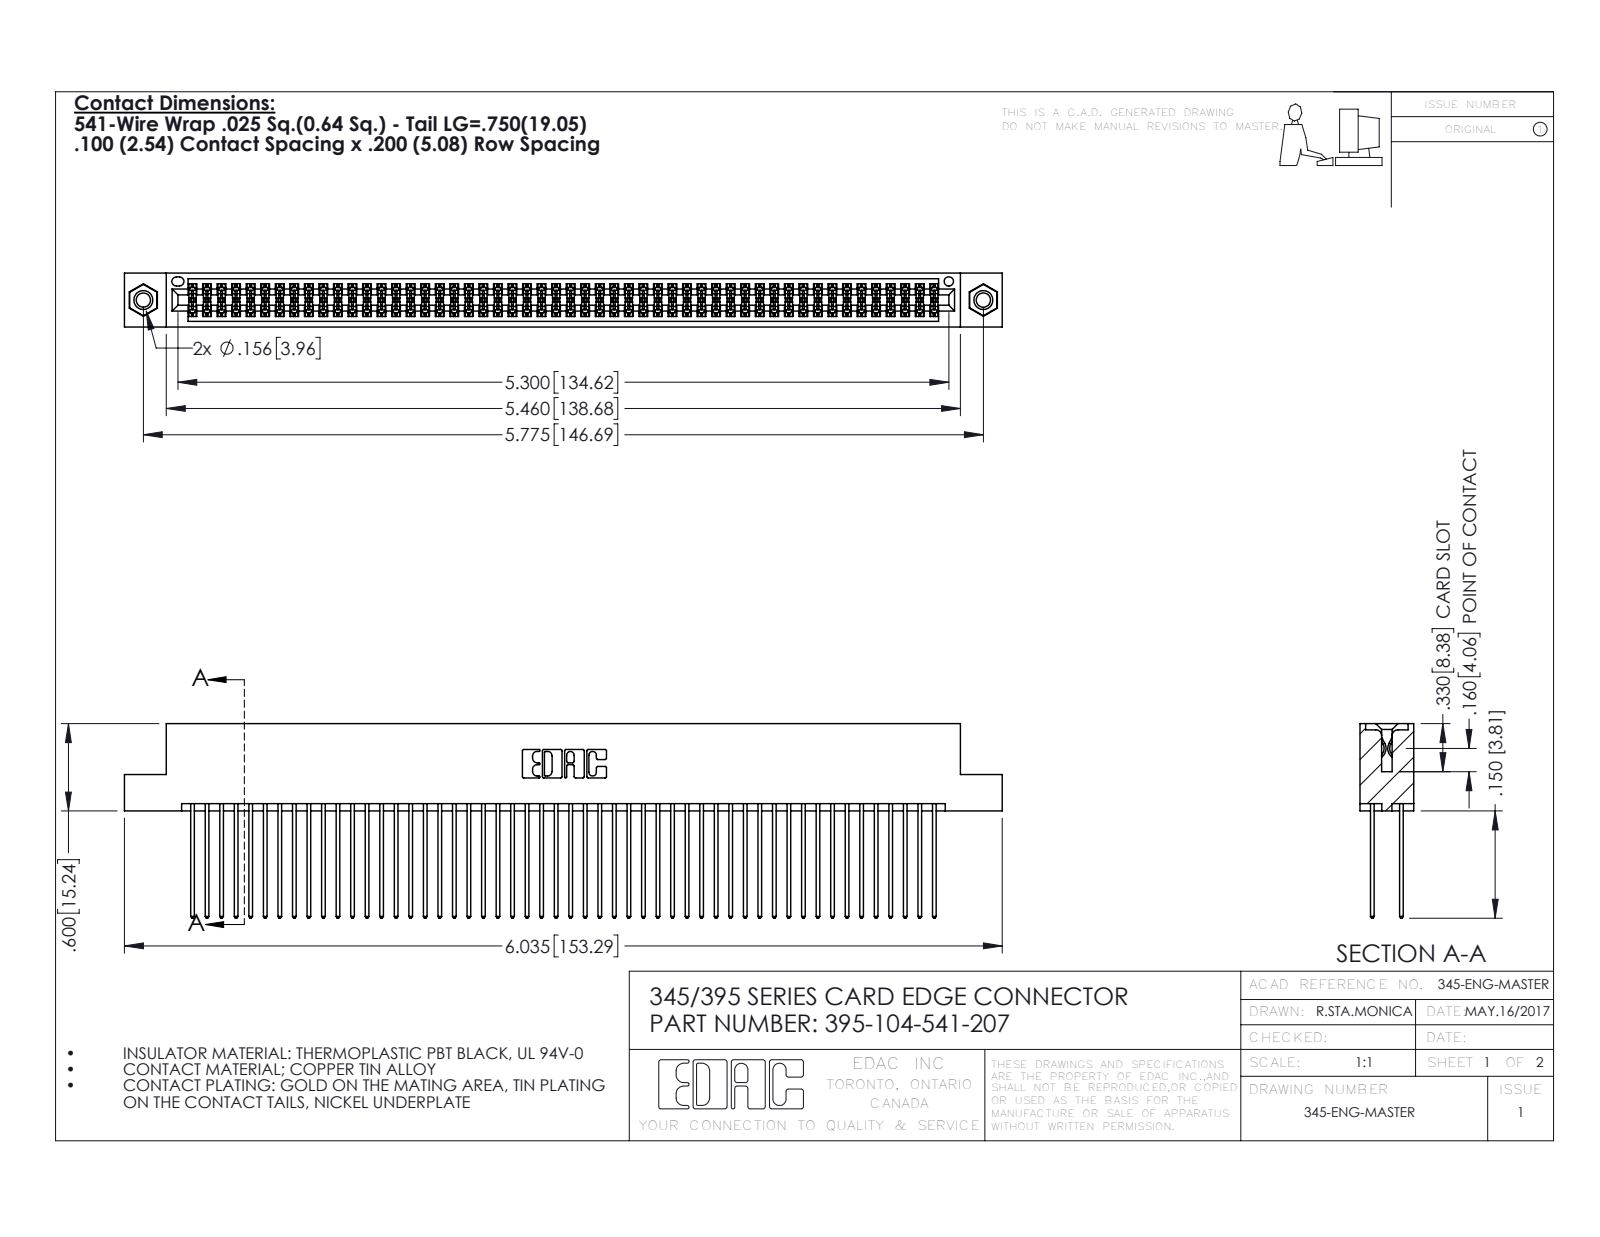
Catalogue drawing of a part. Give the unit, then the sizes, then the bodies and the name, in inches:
Units: inches
Overall size (bounding box): 6.035 × 1.337 × 0.37
Round holes (diameter × count): ⌀0.098 ×2, ⌀0.125 ×2, ⌀0.156 ×2, ⌀0.064 ×1
Round bosses / shafts (diameter × count): ⌀0.155 ×2
Partial cylindrical surfaces — rounded edges, fillets, slot ends (radius × count): R0.006 ×156, R0.01 ×104, R0.01 ×22, R0.007 ×6, R0.031 ×6, R0.026 ×3, R0.014 ×2, R0.019 ×2
Main face-to-face distances: 0.072, 0.298, 0.2, 0.098, 0.272, 0.025, 0.225, 0.37, 0.175, 0.149
Hole centre spacings: 0.27, 5.539, 5.775
Volume: 0.95 in³ · Surface area: 40.36 in²
Bodies: 107 solids, 5386 faces (3544 planar, 1826 cylindrical, 16 other)
Part name (STEP PRODUCT): 345-250-001_345-250-005-103; 345 Part_Flush Mounting Lugs - 0.156 Dia-TI; 395-104-541-207; 345-292-001_345-293-141
STEP written by: SolidWorks 2016 (CONFIG_CONTROL_DESIGN)
